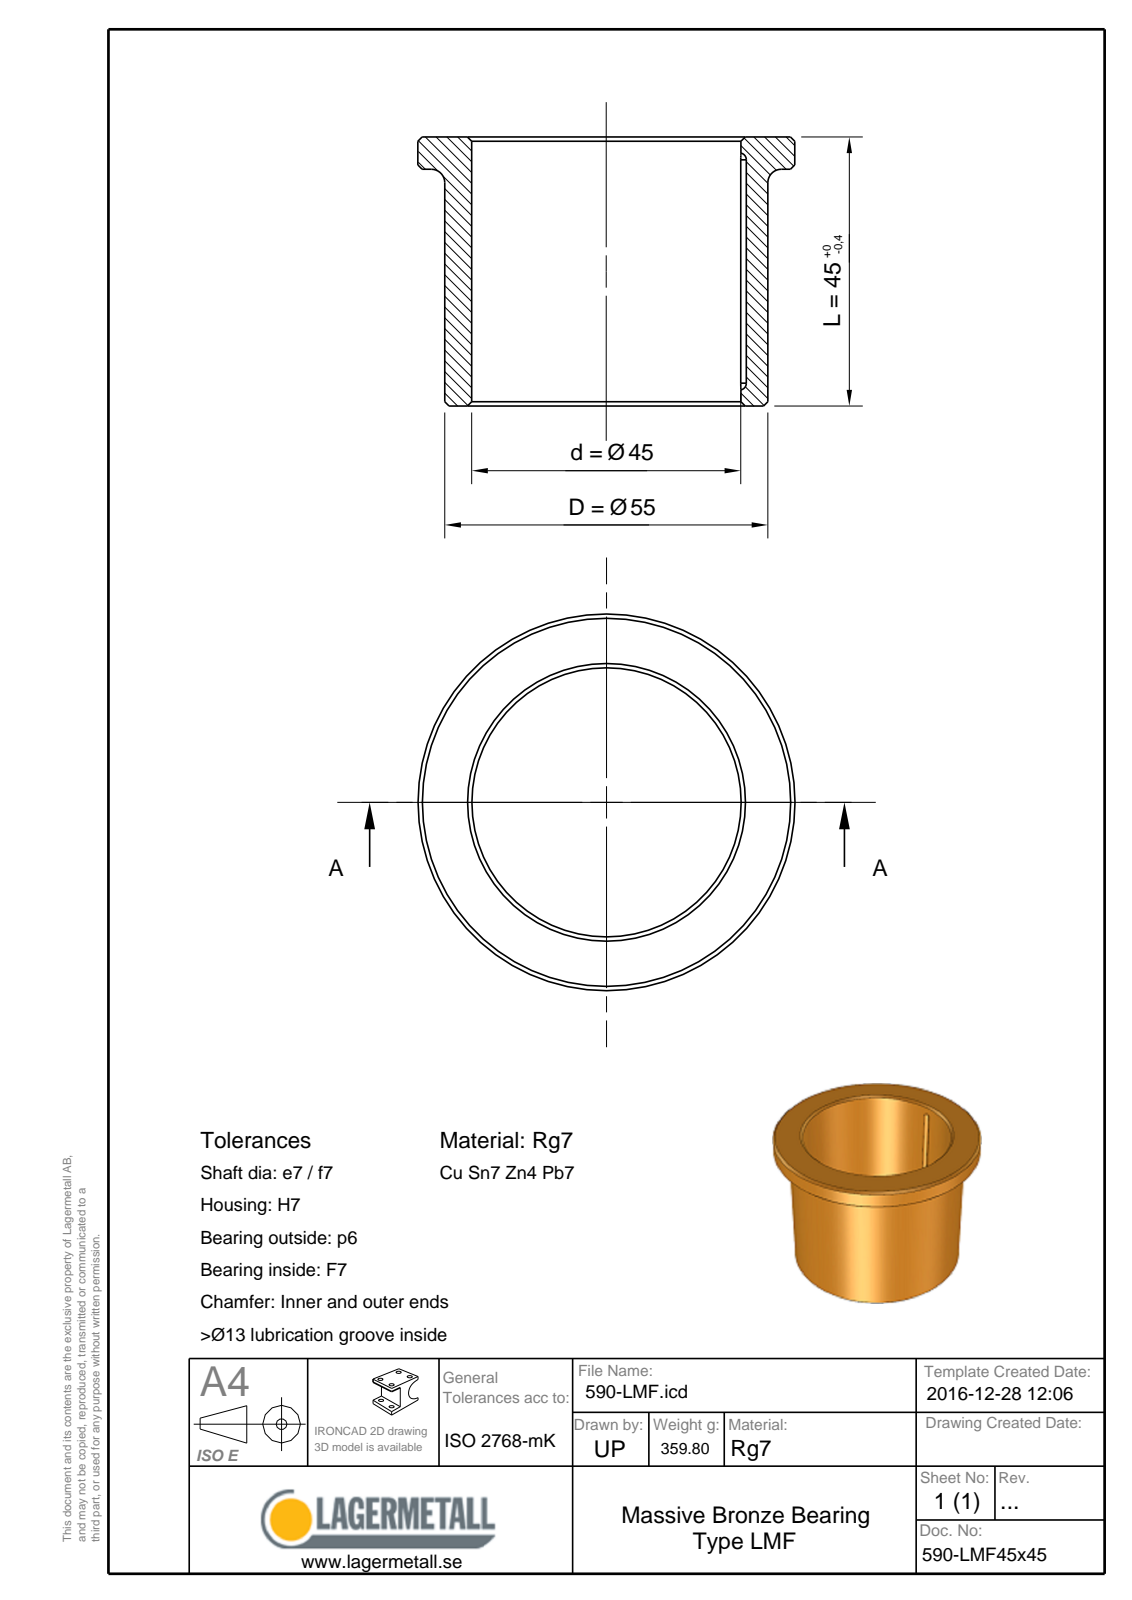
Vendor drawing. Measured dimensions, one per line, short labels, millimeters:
name: 590-LMF45x45
written by: Spatial InterOp 3D (CONFIG_CONTROL_DESIGN)
unit: mm
bodies: 1 solid, 17 faces (4 planar, 5 cylindrical, 8 other)
size: 65 × 65 × 45
volume: 40 886 mm³; area: 17 234 mm²
holes: 1× ⌀45
bosses: 1× ⌀65, 1× ⌀55
rounds: 2× R1.25
face distances: 45, 39, 6
